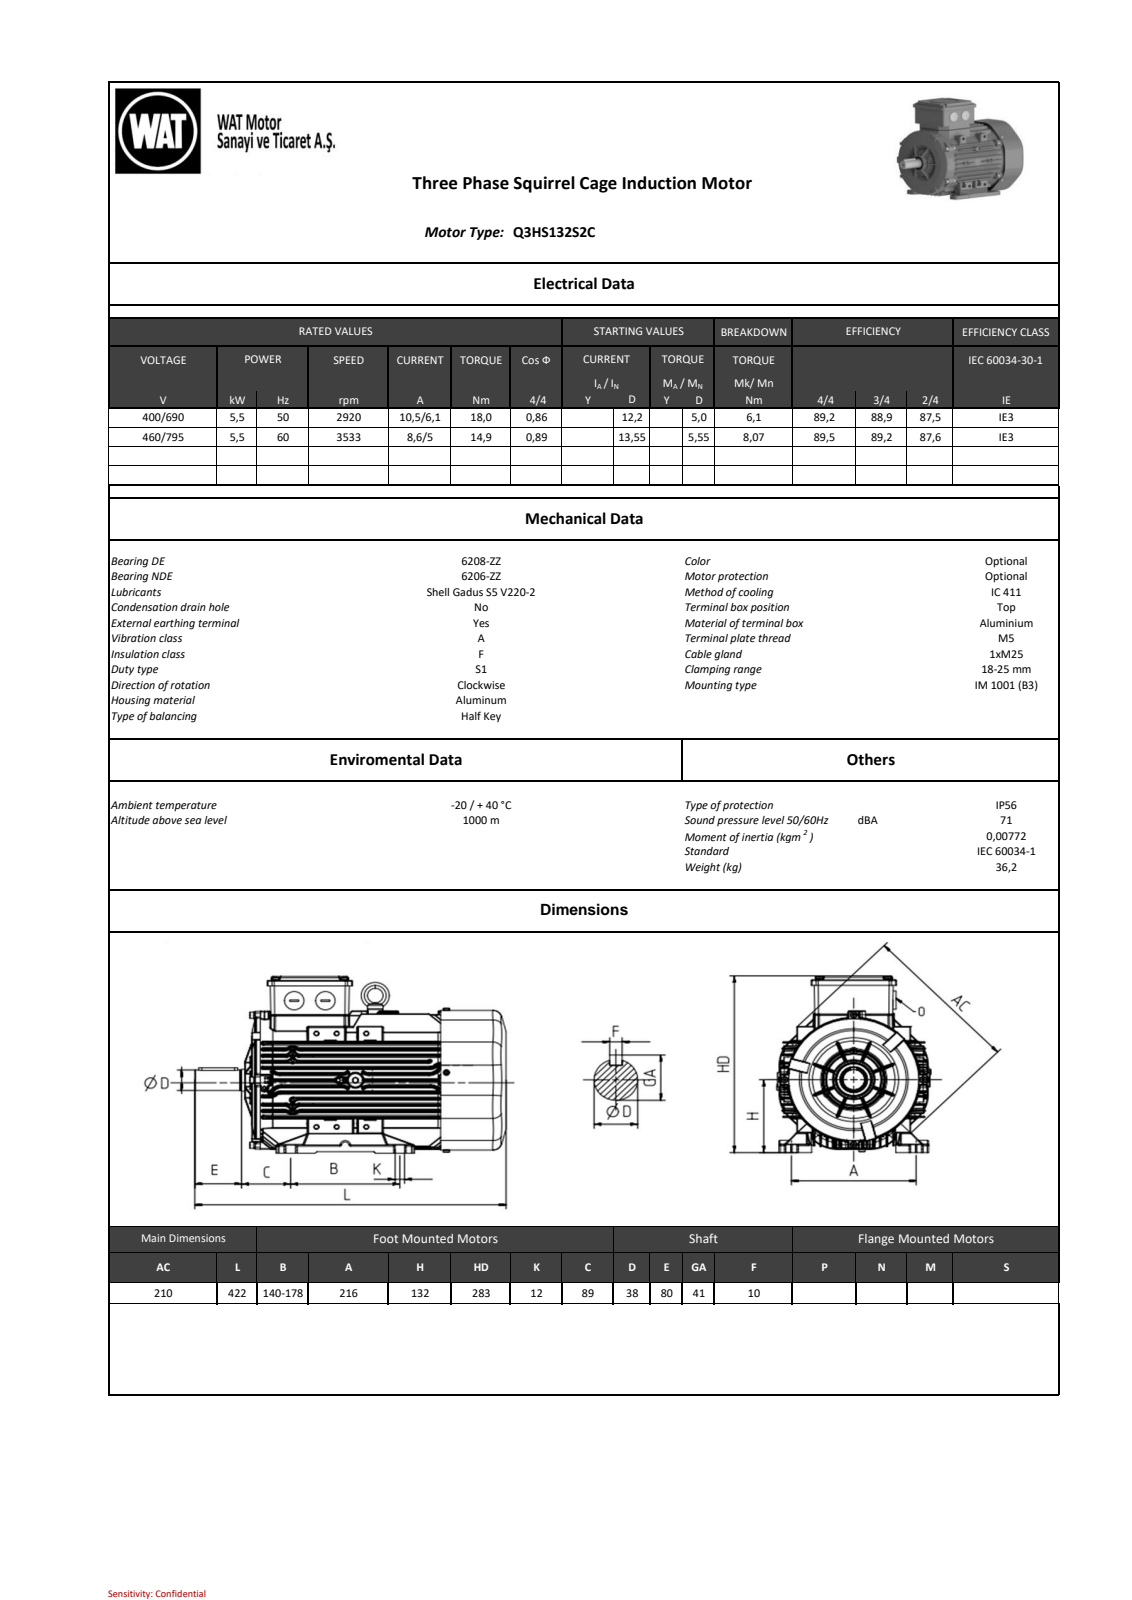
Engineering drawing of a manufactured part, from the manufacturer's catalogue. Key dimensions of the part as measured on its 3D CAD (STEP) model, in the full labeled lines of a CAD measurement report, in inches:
Part name (STEP PRODUCT): Ar311510F8055387
STEP written by: SIEMENS PLM Software NX 9.0 (AUTOMOTIVE_DESIGN)
Units: inches
Bodies: 0 solids, 10930 faces (2461 planar, 3291 cylindrical, 5178 other)
Overall size (bounding box): 16.614 × 11.141 × 9.633
Round holes (diameter × count): ⌀0.262 ×4, ⌀0.327 ×4, ⌀0.197 ×3, ⌀0.472 ×2, ⌀0.984 ×2, ⌀1.094 ×2, ⌀0.13 ×1, ⌀0.157 ×1, ⌀0.186 ×1, ⌀0.194 ×1, ⌀0.256 ×1, ⌀0.315 ×1
Round bosses / shafts (diameter × count): ⌀0.315 ×12, ⌀0.583 ×4, ⌀0.512 ×4, ⌀0.465 ×4, ⌀0.394 ×4, ⌀0.236 ×4, ⌀0.079 ×3, ⌀7.402 ×1
Partial cylindrical surfaces — rounded edges, fillets, slot ends (radius × count): R0.02 ×759, R0.031 ×505, R0.039 ×488, R0.079 ×230, R0.118 ×45, R0.012 ×27, R0.197 ×14, R0.015 ×10
Main face-to-face distances: 0.197, 0.039, 0.846, 1.416, 0.433, 3.919, 0.983, 4.444, 0.321, 2.714
Hole centre spacings: 1.575, 4.331, 1.949, 2.278, 2.859, 2.962, 4.562, 4.867
